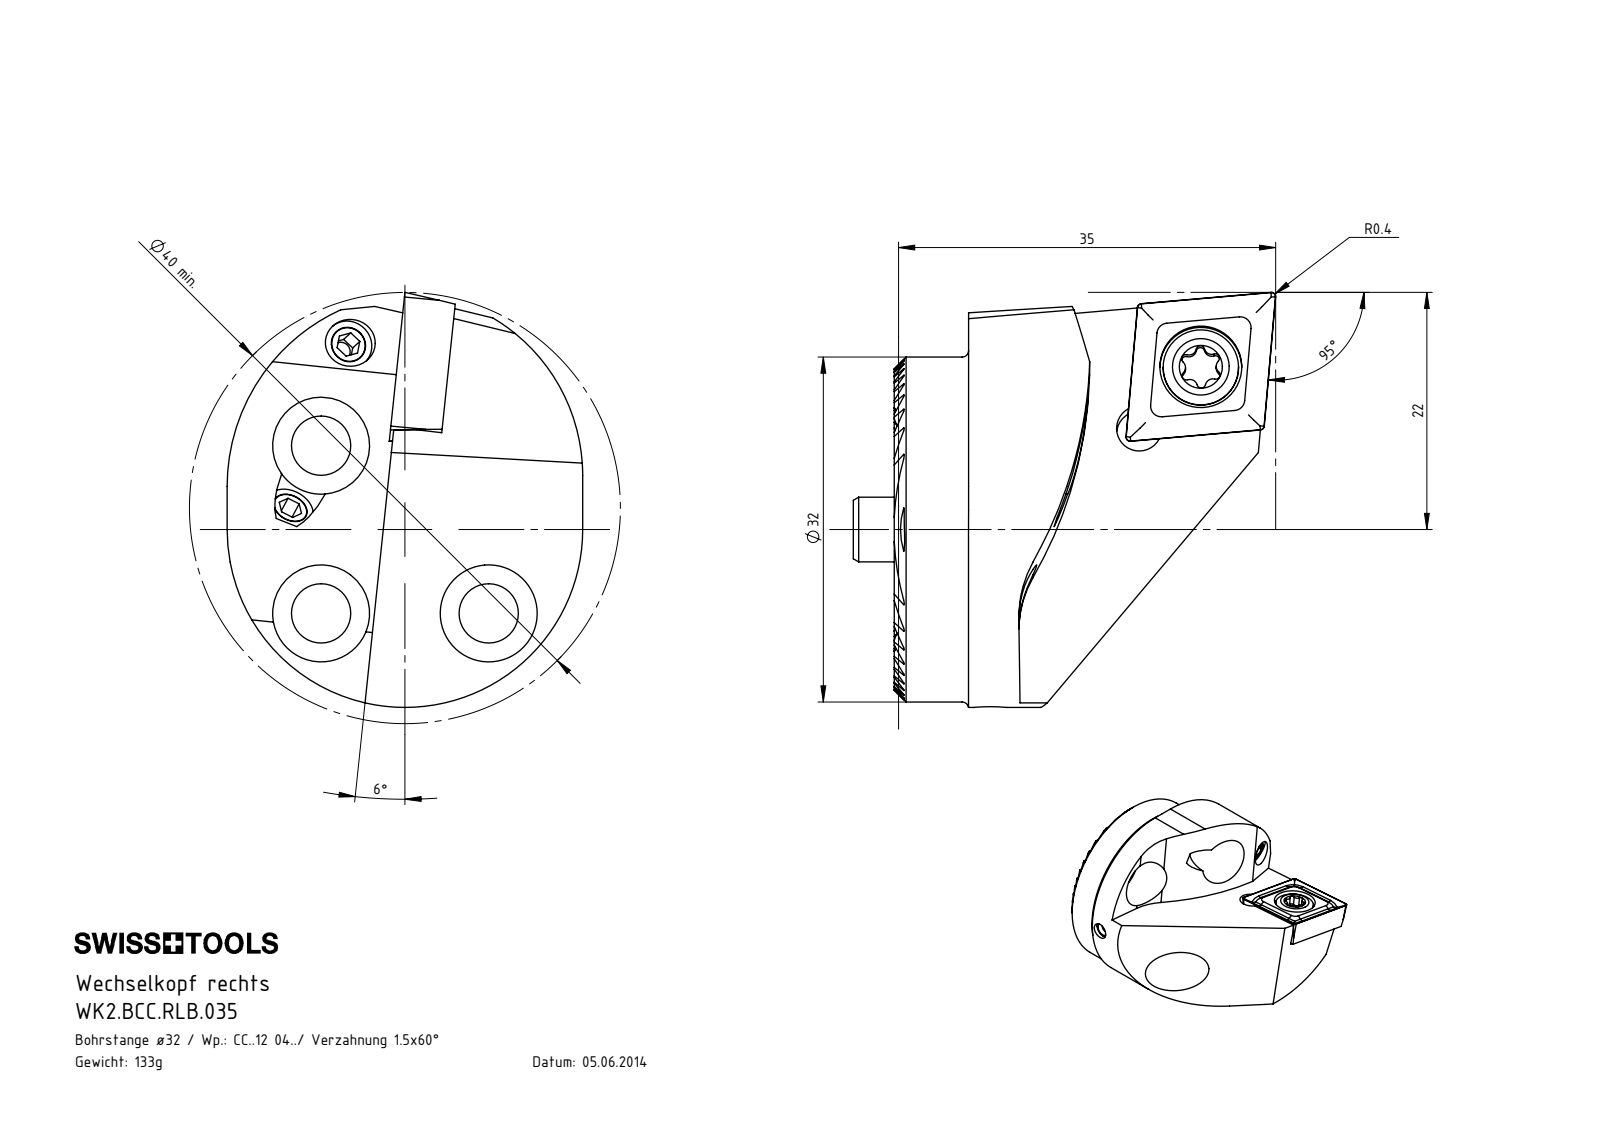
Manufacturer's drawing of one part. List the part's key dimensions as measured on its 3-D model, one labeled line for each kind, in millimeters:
Part name (STEP PRODUCT): WK2-ER1.001.012_A_Fertigbearbeitung; WKX-ER1.004.005_A_PreviewCfg; CCMT120404; WK2.BCC.RLB.035 (+3 more)
STEP written by: SolidWorks 2017 (AUTOMOTIVE_DESIGN)
Units: millimetres
Bodies: 12 solids, 553 faces (193 planar, 189 cylindrical, 171 other)
Overall size (bounding box): 39.2 × 38.5 × 33
Volume: 16 982 mm³ · Surface area: 8 752 mm²
Round holes (diameter × count): ⌀5.5 ×4, ⌀2.38 ×3, ⌀2.5 ×3, ⌀4.2 ×3, ⌀9 ×3, ⌀1.7 ×2, ⌀3 ×2, ⌀3.3 ×2, ⌀4.5 ×2, ⌀7.6 ×1, ⌀12 ×1
Round bosses / shafts (diameter × count): ⌀3 ×3, ⌀4 ×2, ⌀32 ×1, ⌀7 ×1, ⌀6 ×1, ⌀5 ×1
Partial cylindrical surfaces — rounded edges, fillets, slot ends (radius × count): R0.12 ×22, R0.39 ×6, R0.69 ×3, R0.69 ×3, R16.5 ×1, R17 ×1, R18 ×1
Main face-to-face distances: 1.3, 2.6, 3.9, 5.2, 6.5, 12.99, 11.69, 14.29, 7.8, 10.39
Hole centre spacings: 11, 8.09, 15.56, 22.01
